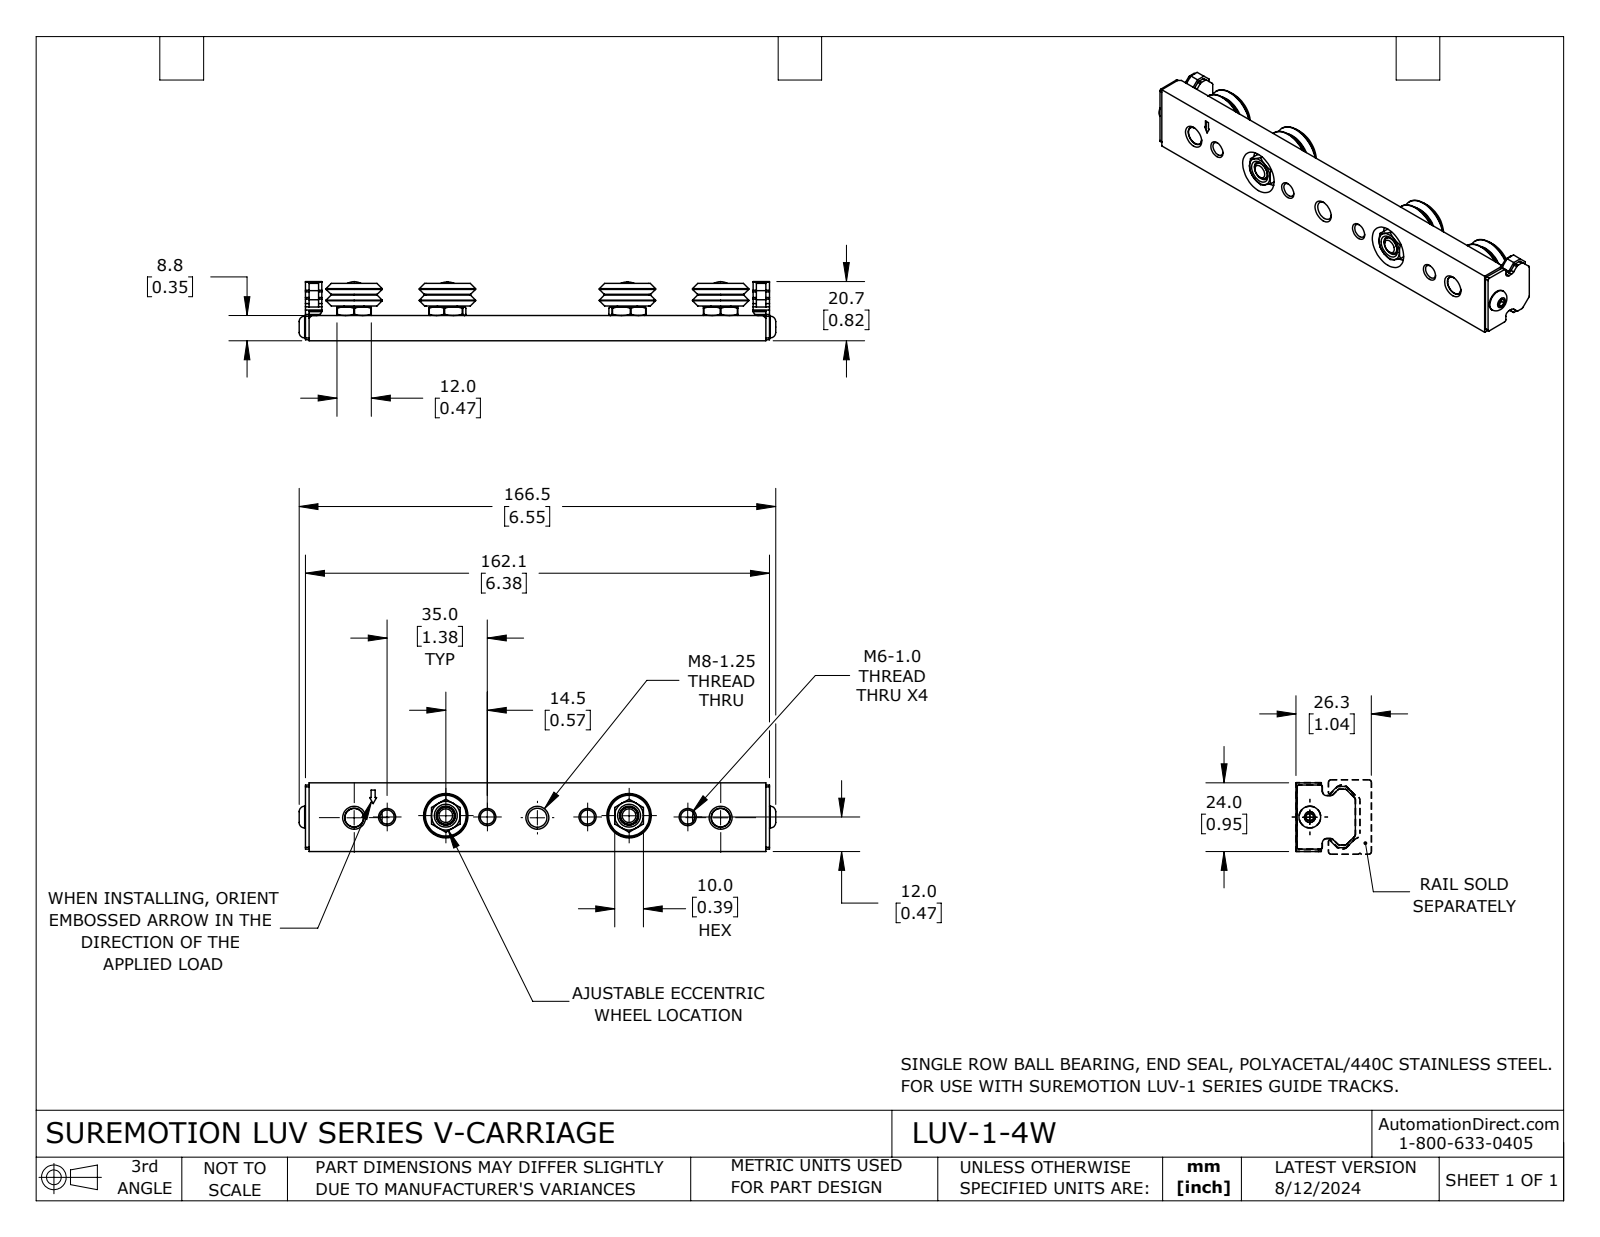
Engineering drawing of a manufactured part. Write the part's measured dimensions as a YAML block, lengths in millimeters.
part_name: "LUV-1-4W"
step_written_by: "SolidWorks 2023 (CONFIG_CONTROL_DESIGN)"
units: millimeters
bodies: {solids: 9, faces: 824, planar: 242, cylindrical: 244, other: 338}
overall_size: [166.45, 24, 20.73]
volume: 43759
surface_area: 23020
round_holes:
  - {diameter: 4.76, count: 4}
  - {diameter: 4.92, count: 4}
  - {diameter: 6.65, count: 4}
  - {diameter: 12.18, count: 4}
  - {diameter: 12.41, count: 4}
  - {diameter: 6.36, count: 2}
  - {diameter: 15.49, count: 2}
  - {diameter: 3.24, count: 1}
  - {diameter: 6.65, count: 1}
round_bosses_or_shafts:
  - {diameter: 19.58, count: 4}
  - {diameter: 8.46, count: 4}
  - {diameter: 8.23, count: 4}
  - {diameter: 4.75, count: 4}
  - {diameter: 14.25, count: 2}
  - {diameter: 8, count: 2}
  - {diameter: 6.3, count: 2}
  - {diameter: 6, count: 2}
partial_cylinders:
  - {radius: 0.38, count: 12}
  - {radius: 0.84, count: 6}
  - {radius: 0.64, count: 4}
  - {radius: 1.6, count: 4}
  - {radius: 6.84, count: 4}
  - {radius: 1.78, count: 2}
face_to_face_distances: [8.81, 24, 1.27, 160.79, 6.14, 7.65, 2.67, 11.23, 13.9, 20.04]
hole_center_spacings: [35, 0.61, 13.93, 14.51, 20.51, 21.07, 48.93, 49.5]
